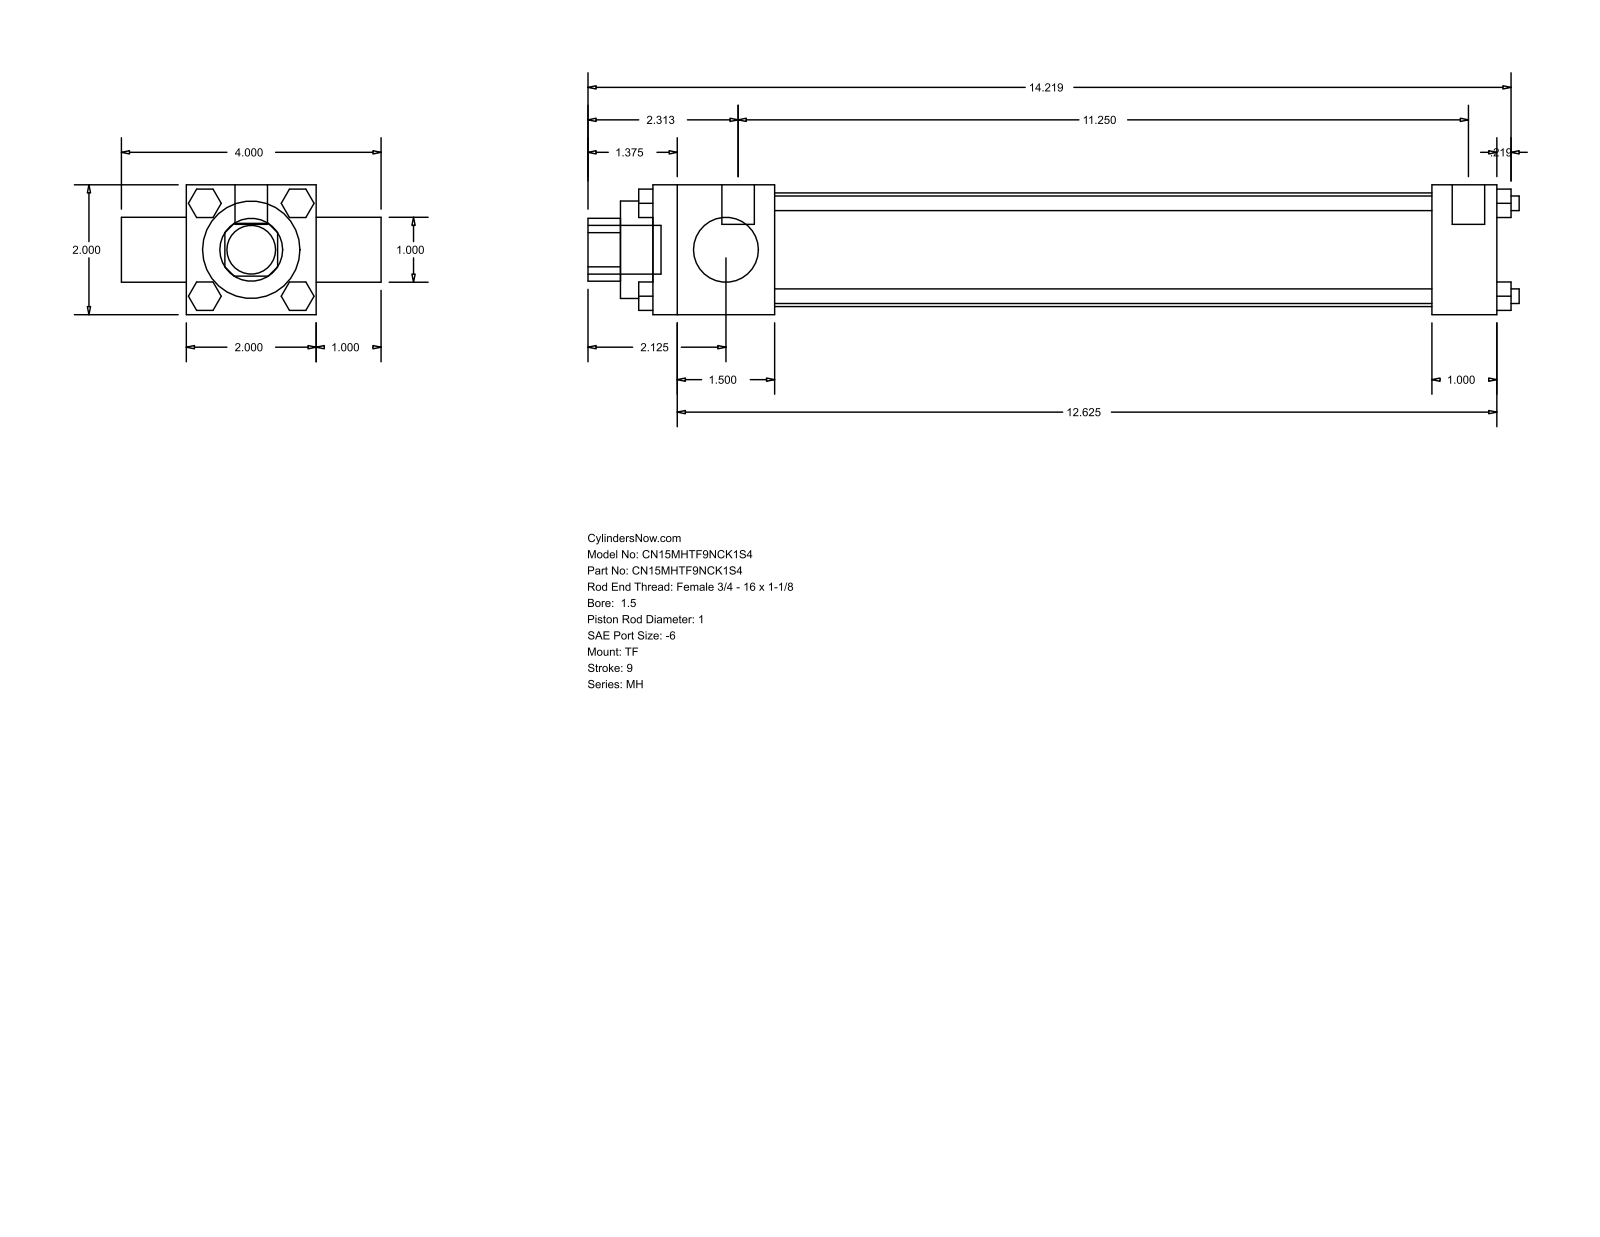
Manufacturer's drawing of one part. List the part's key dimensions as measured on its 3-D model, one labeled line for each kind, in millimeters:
Part name (STEP PRODUCT): MH_TF__0150_1
STEP written by: GSSL Pune (CONFIG_CONTROL_DESIGN)
Units: millimetres
Bodies: 0 solids, 120 faces (92 planar, 28 cylindrical, 0 other)
Overall size (bounding box): 364.33 × 101.6 × 50.8
Round holes (diameter × count): ⌀25.4 ×2, ⌀38.1 ×1, ⌀44.45 ×1
Round bosses / shafts (diameter × count): ⌀5.71 ×4, ⌀5.56 ×3, ⌀12.7 ×2, ⌀19.05 ×1
Partial cylindrical surfaces — rounded edges, fillets, slot ends (radius × count): R12.29 ×1
Main face-to-face distances: 50.8, 25.4, 330.2, 76.2, 47.63, 282.57, 304.8, 257.17, 335.76, 12.7
